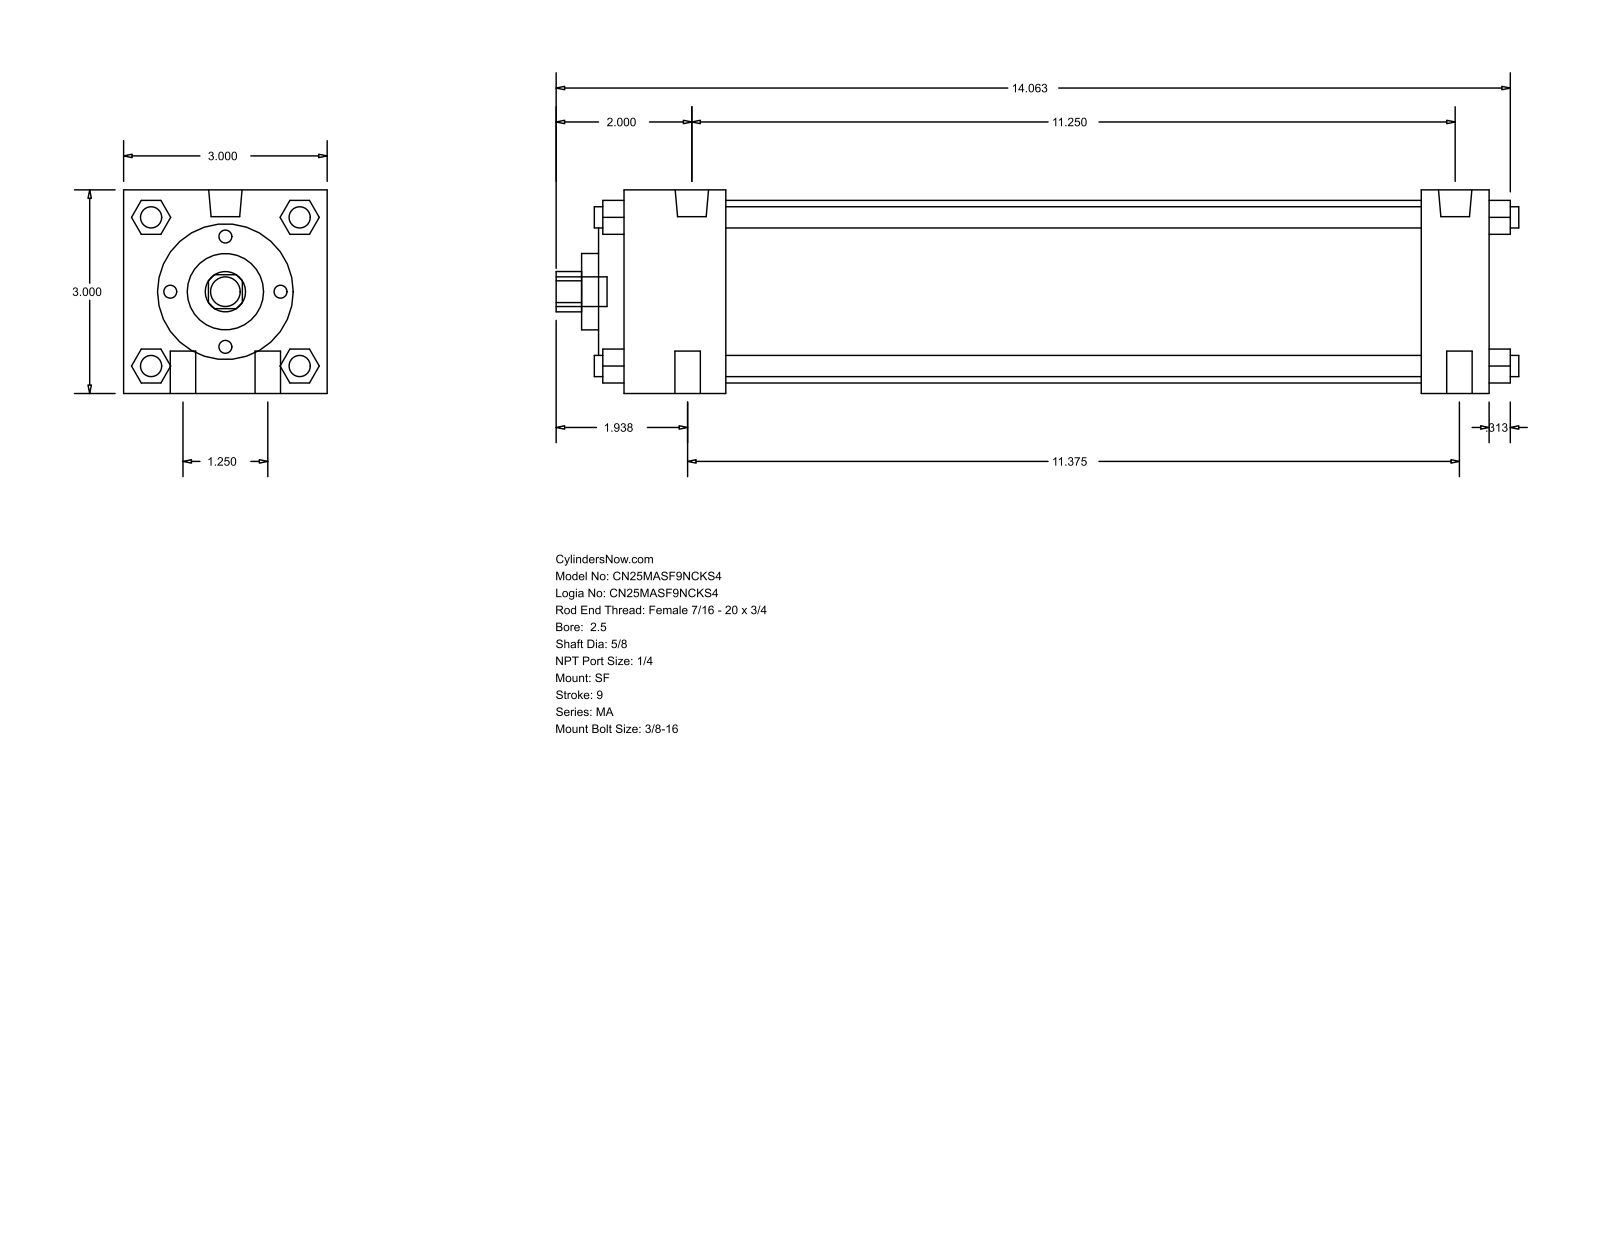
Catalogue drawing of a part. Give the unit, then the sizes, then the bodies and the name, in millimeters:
Units: millimetres
Overall size (bounding box): 360.36 × 76.2 × 76.2
Round holes (diameter × count): ⌀15.88 ×1, ⌀28.57 ×1, ⌀50.8 ×1, ⌀68.33 ×1
Round bosses / shafts (diameter × count): ⌀7.94 ×6, ⌀9.53 ×4, ⌀12.49 ×2, ⌀11.11 ×1
Partial cylindrical surfaces — rounded edges, fillets, slot ends (radius × count): R7.54 ×1
Main face-to-face distances: 76.2, 323.85, 25.4, 298.45, 38.1, 260.35, 285.75, 12.7, 9.52, 47.62
Bodies: 0 solids, 126 faces (95 planar, 31 cylindrical, 0 other)
Part name (STEP PRODUCT): MA_SF__0250_0.625
STEP written by: GSSL Pune (CONFIG_CONTROL_DESIGN)
